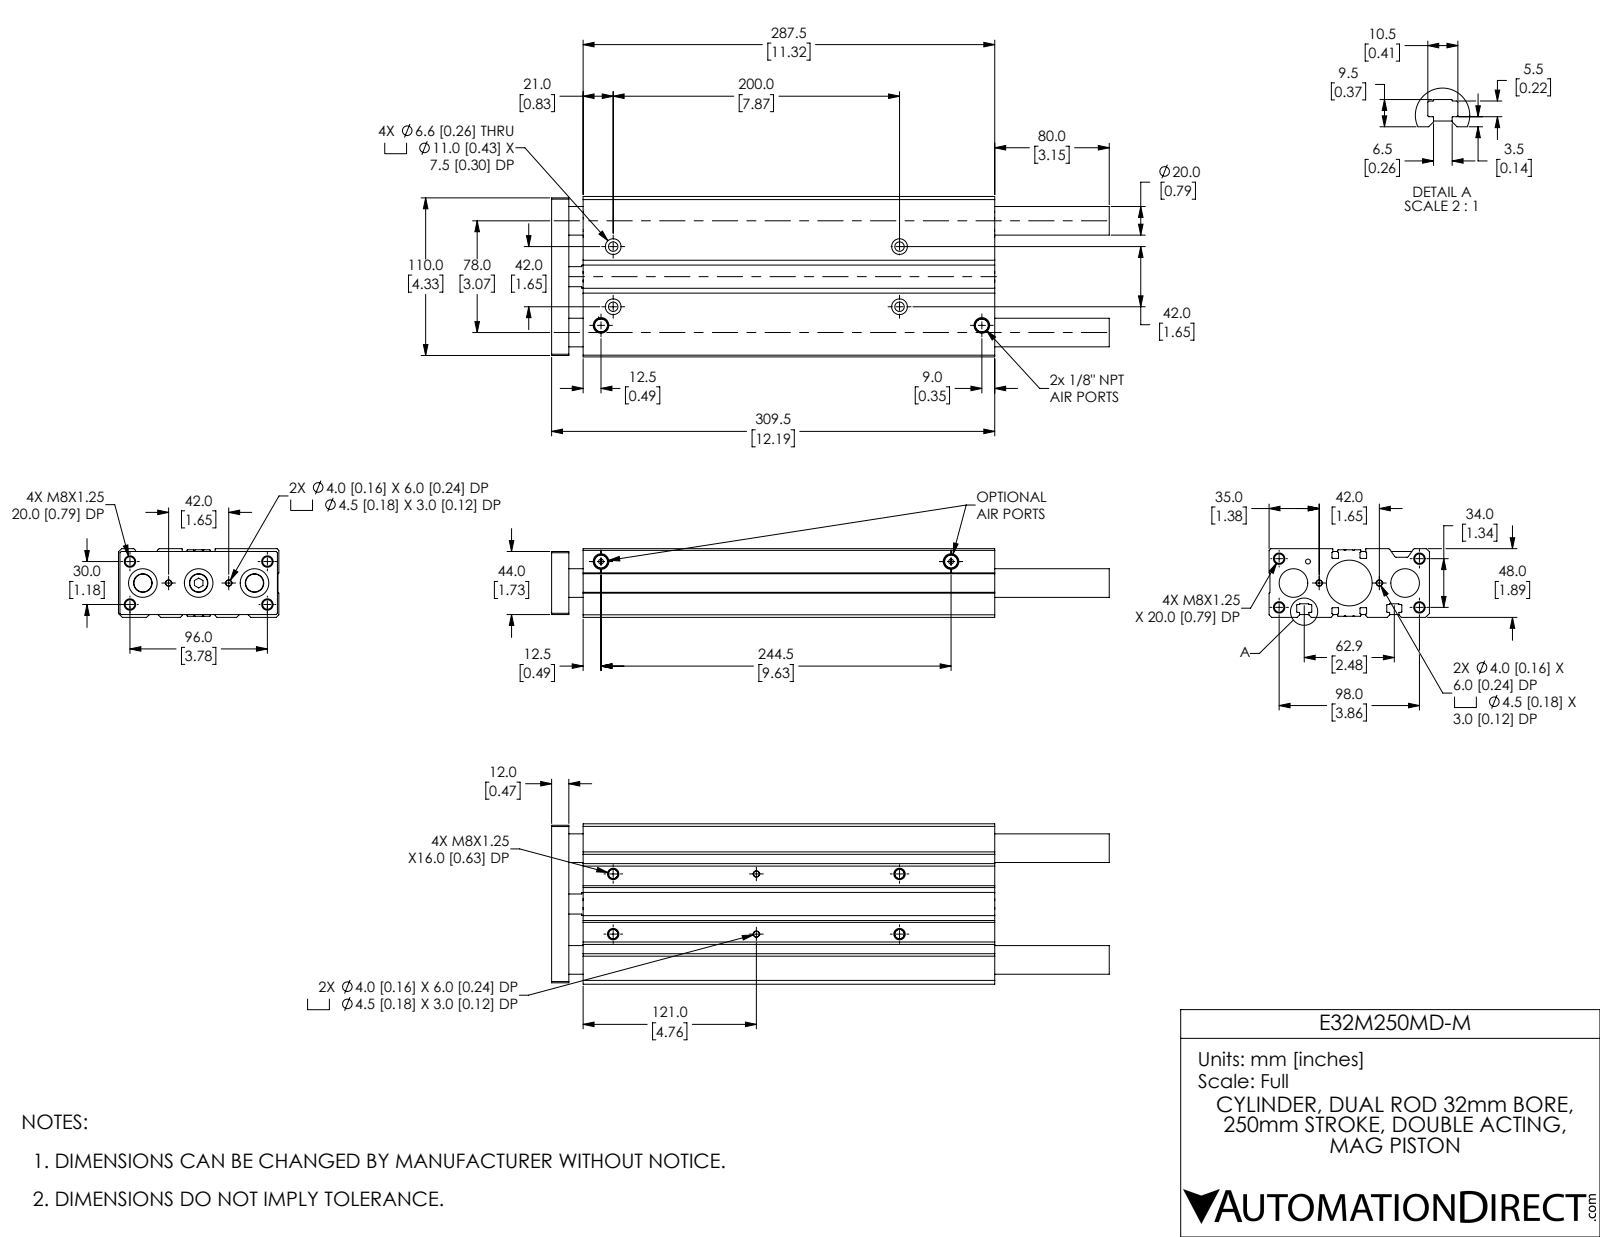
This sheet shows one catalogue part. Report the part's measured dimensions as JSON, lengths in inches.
{"part_name": "E32M250MD-M; E32M250MD-M_ENDPLATE; E32M250MD-M_BODY", "step_written_by": "SolidWorks 2019 (CONFIG_CONTROL_DESIGN)", "units": "inches", "bodies": {"solids": 5, "faces": 423, "planar": 139, "cylindrical": 190, "other": 94}, "overall_size": [15.335, 4.409, 1.89], "volume_in3": 83.79, "surface_area_in2": 446.5, "round_holes": [[0.262, 12], [0.157, 4], [0.177, 4], [0.26, 4], [0.433, 4], [0.135, 3], [0.394, 3], [0.787, 3], [0.51, 2], [0.787, 1], [1.26, 1], [1.26, 1]], "round_bosses_or_shafts": [[0.63, 1], [0.51, 1]], "partial_cylinders_radius": [[0.008, 32], [0.016, 28], [0.047, 4], [0.012, 2]], "face_to_face_distances": [1.89, 0.031, 0.236, 4.409, 1.858, 1.484, 1.622, 0.024, 1.516, 0.772], "hole_center_spacings": [0.088, 0.689, 0.776, 1.216, 1.261, 1.29, 1.654, 1.98]}
